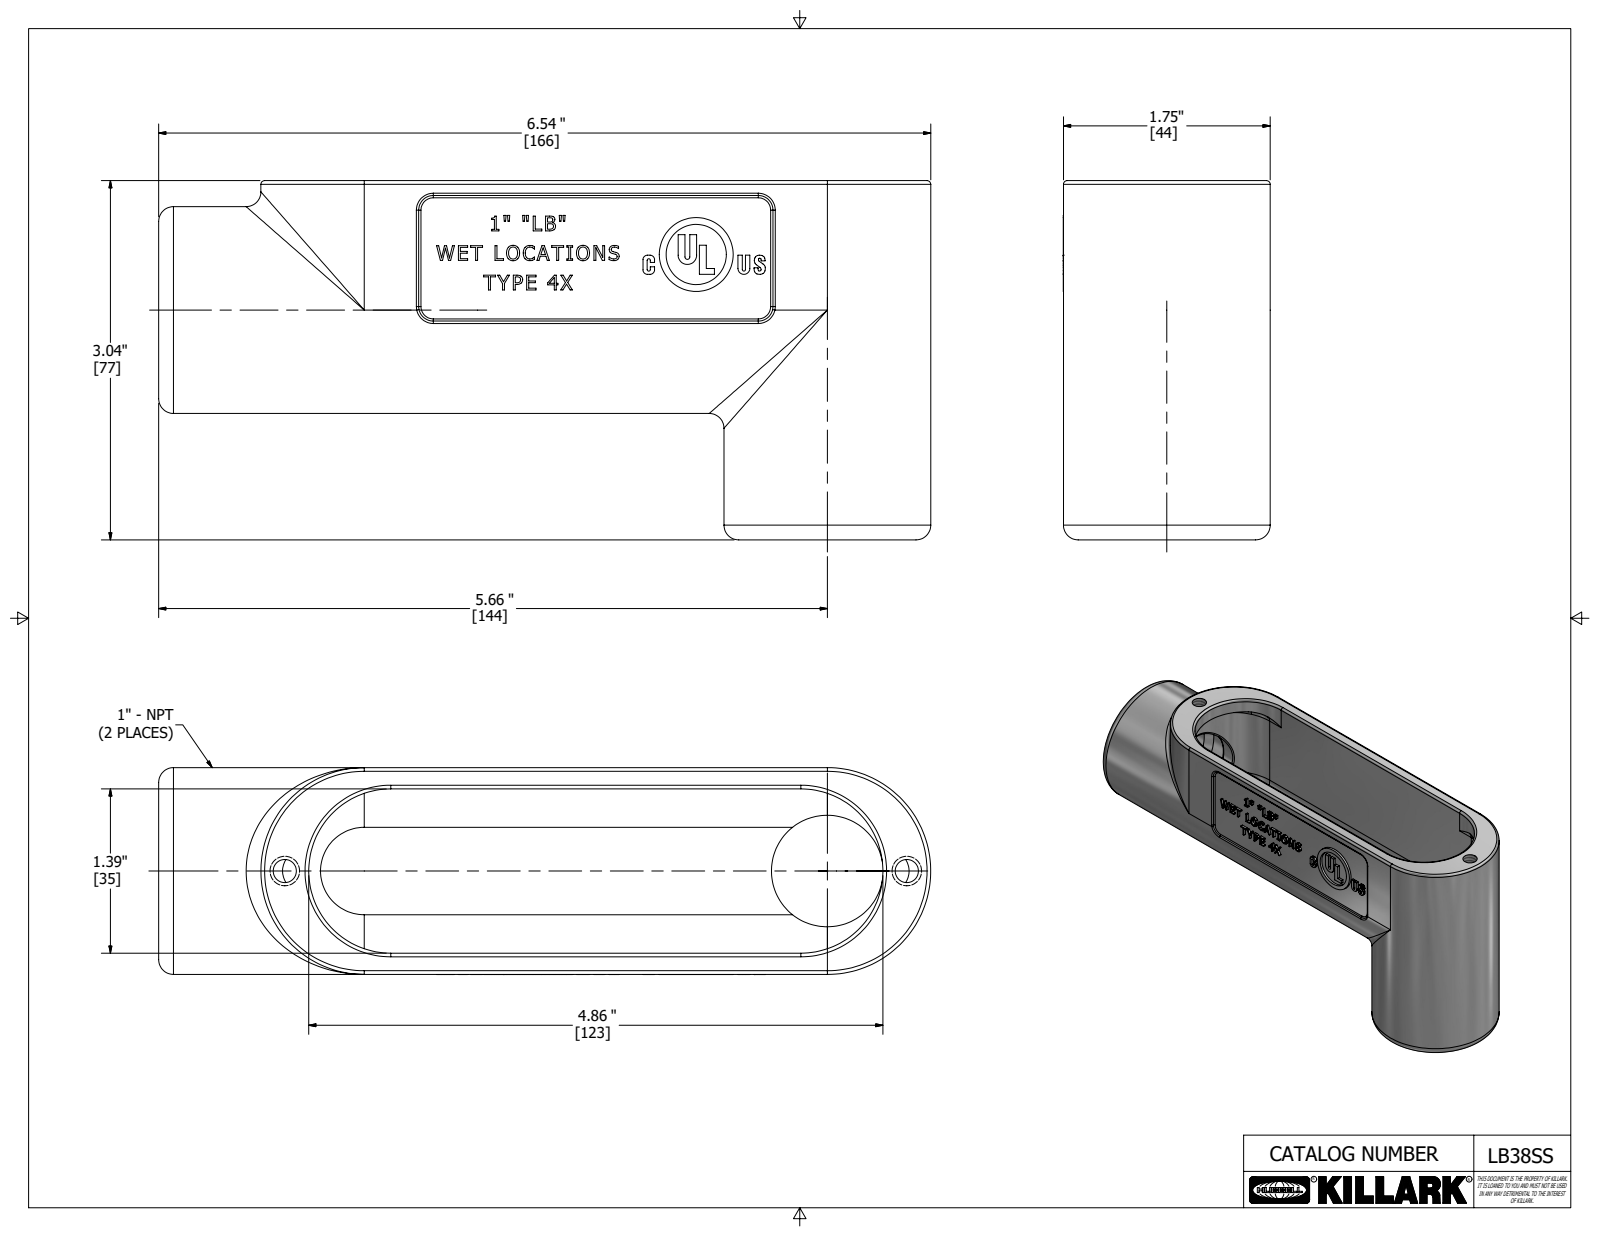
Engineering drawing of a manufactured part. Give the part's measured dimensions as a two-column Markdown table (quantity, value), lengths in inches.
| quantity | value |
| --- | --- |
| part name | LB38SS |
| STEP written by | Autodesk Inventor 2020 (AUTOMOTIVE_DESIGN) |
| units | inches |
| bodies | 1 solid, 888 faces (534 planar, 70 cylindrical, 284 other) |
| overall size | 6.535 × 3.04 × 1.751 |
| volume | 7.975 in³ |
| surface area | 79.37 in² |
| round holes (diameter × count) | 0.196 × 2, 1.321 × 2, 0.509 × 1 |
| round bosses / shafts (diameter × count) | 1.75 × 2, 0.625 × 1 |
| partial cylindrical surfaces (radius × count) | 0.02 × 8, 0.031 × 5, 0.038 × 4, 0.695 × 4, 0.013 × 2, 0.013 × 2, 0.125 × 2, 0.325 × 2 |
| main face-to-face distances | 0.18, 1.57, 1.39, 1.72, 1.54, 0.15, 1.645, 0.03, 1.75, 0.031 |
| hole center spacings | 0.672, 4.593, 5.265 |
